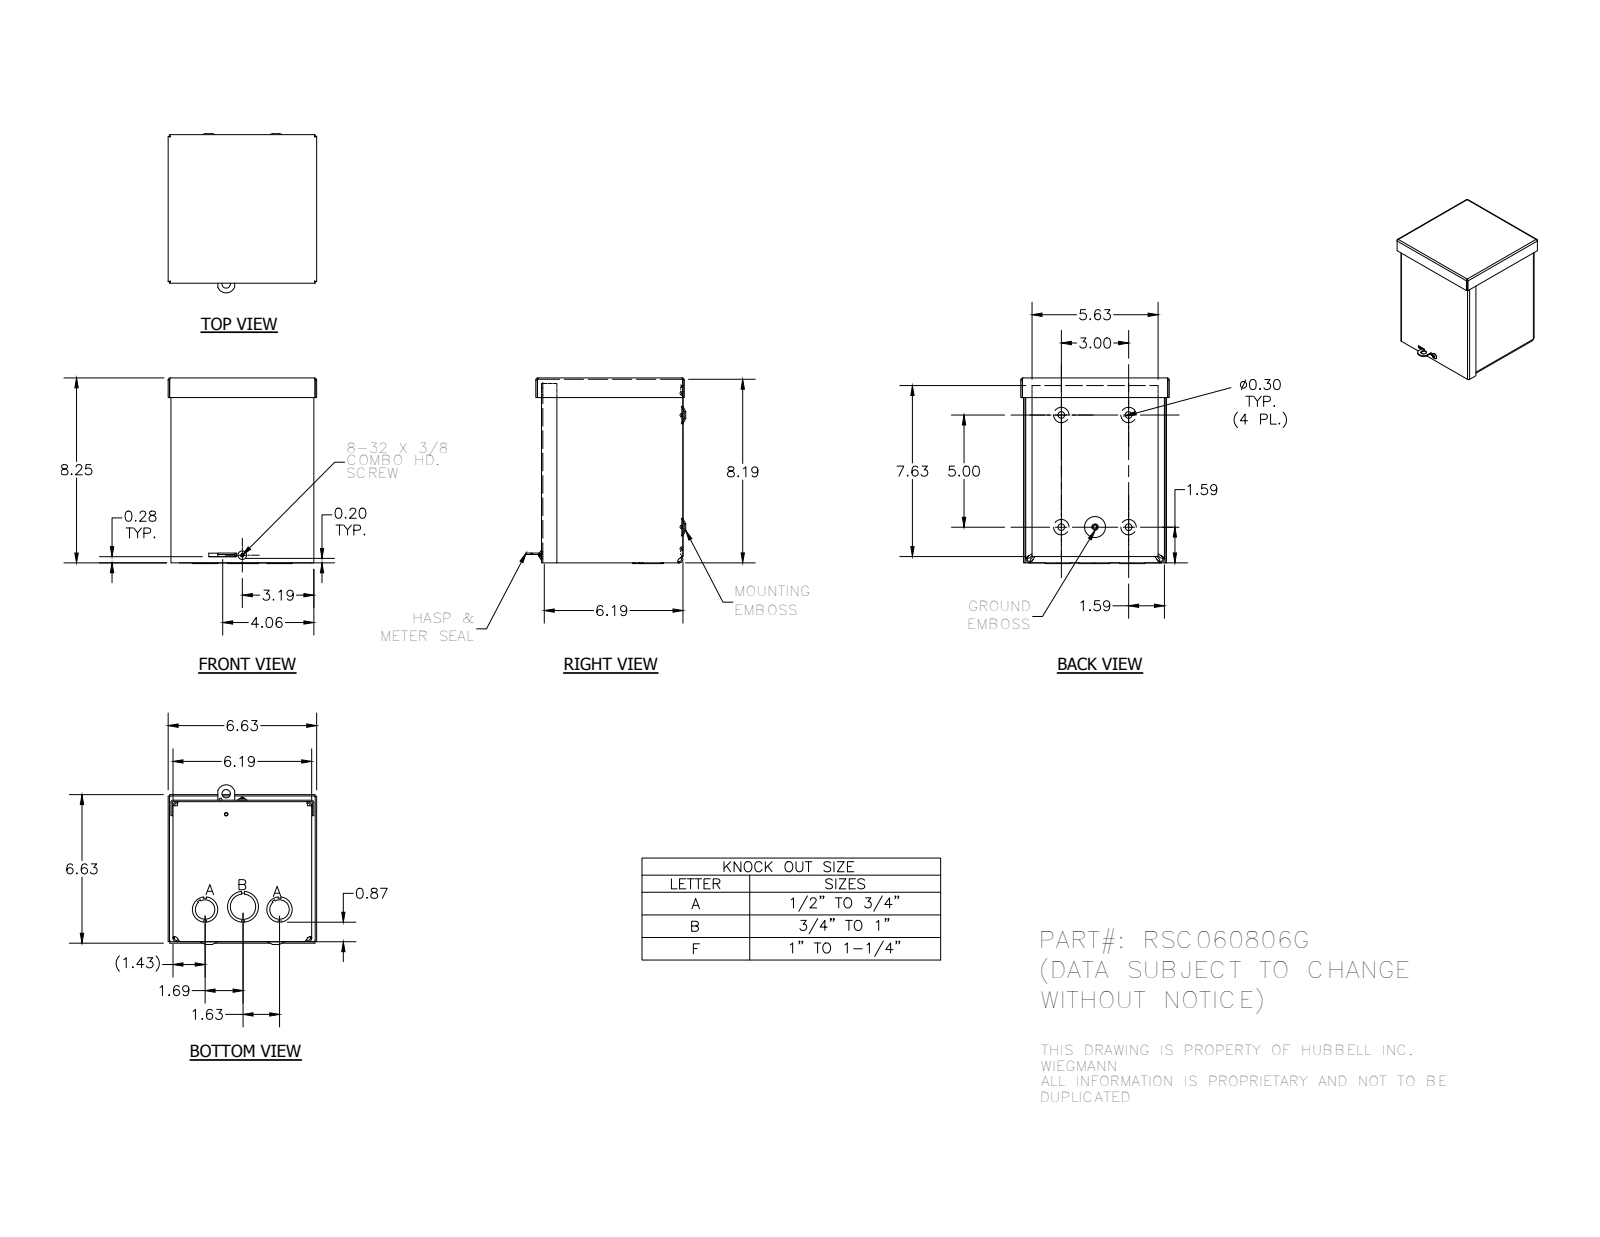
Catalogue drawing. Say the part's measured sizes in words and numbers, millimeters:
The part is named "RSC060806G_WRAP; RSC0608G_LID; RSC0606G_CAP; 3183 (+4 more)". Its 3-D file was written by "Autodesk Inventor 2014 (AUTOMOTIVE_DESIGN)". It is 6 solids with 461 faces: 220 planar, 116 cylindrical and 125 other. Overall it measures 210.32 by 180.97 by 168.28 millimeters. Its volume is 388 097 cubic millimeters and its surface area 501 207 square millimeters. Round holes: 4 of diameter 7.62, 3 of diameter 28.57, 2 of diameter 3.17, 2 of diameter 7.95, 2 of diameter 22.22, 1 of diameter 3.76, 1 of diameter 3.96, 1 of diameter 4.19, 1 of diameter 9.52, 1 of diameter 34.92. Round bosses or shafts: 1 of diameter 9.75, 1 of diameter 5.8, 1 of diameter 4.17. Partial cylindrical surfaces (rounded edges, fillets, slot ends): 10 of radius 0.25, 8 of radius 0.79, 8 of radius 2.37, 8 of radius 3.17, 8 of radius 4.75, 4 of radius 0.53, 4 of radius 0.79, 4 of radius 1.4. The main face-to-face distances are 1.58, 1.57, 155.59, 206.39, 158.73, 154.01, 157.17, 3.15, 157.15, 1.59. The hole center spacings are 38.1, 76.2, 127, 132.58, 148.11, 9.1, 17.84, 23.19.
